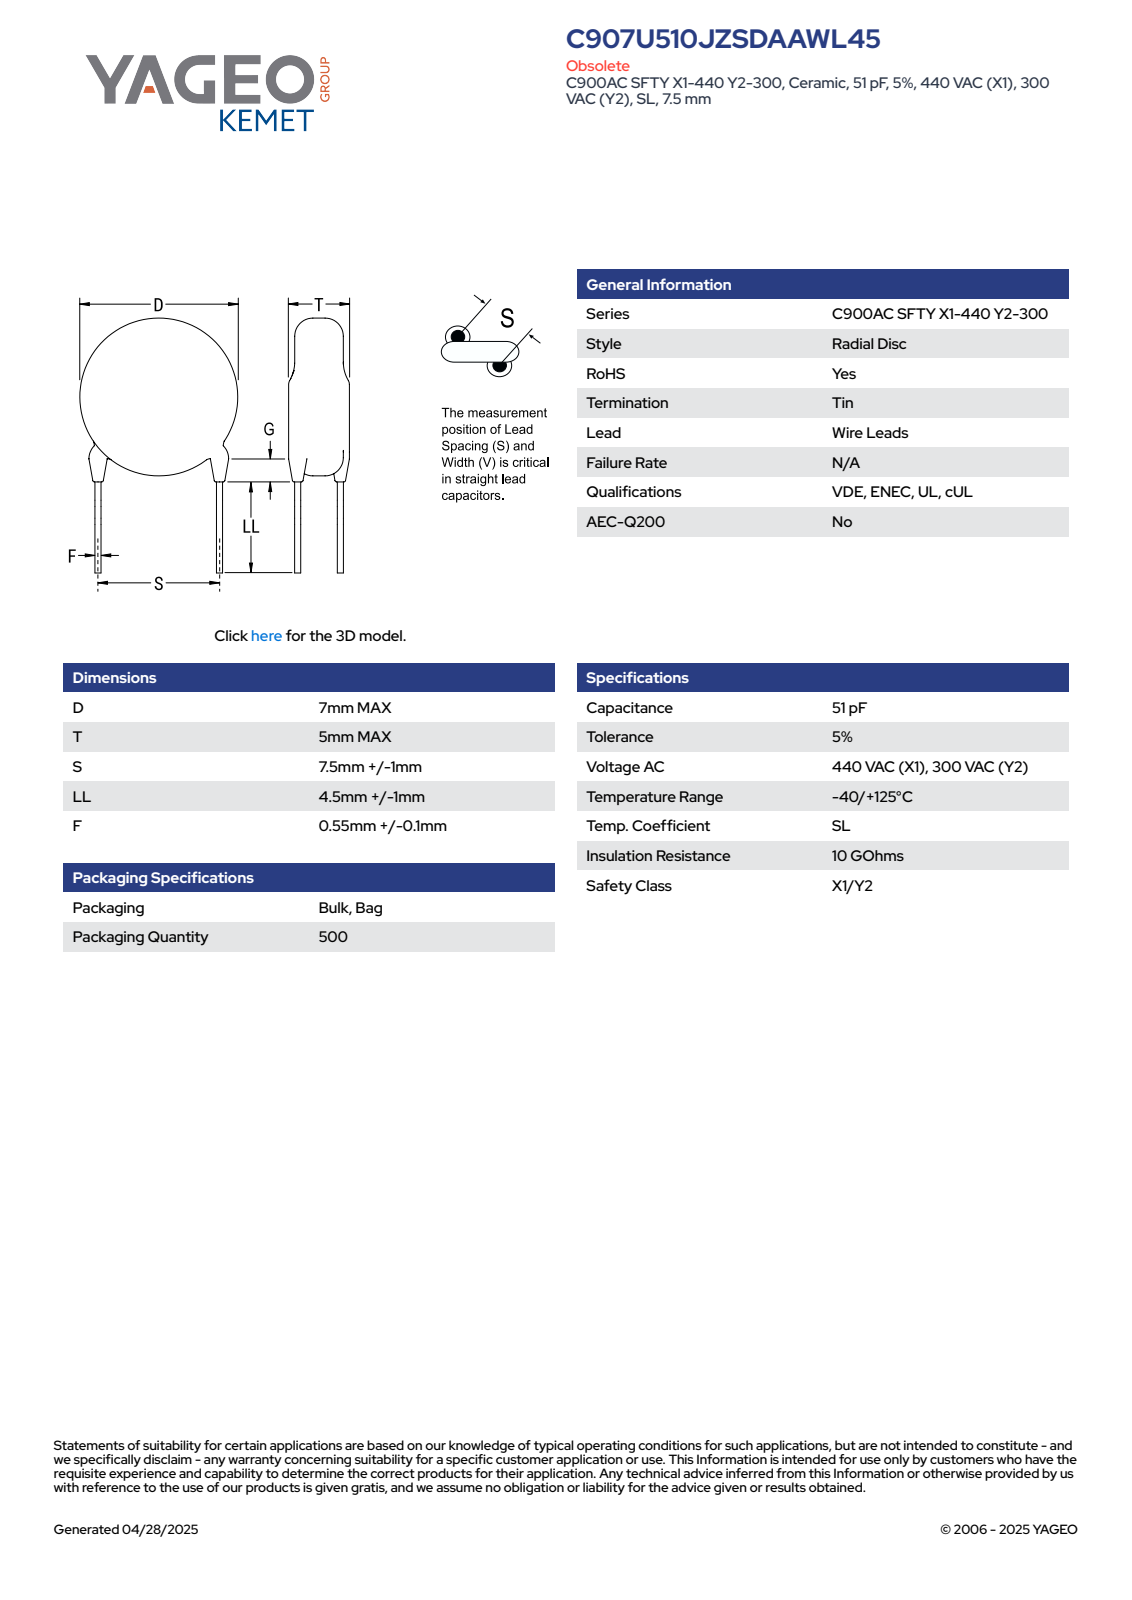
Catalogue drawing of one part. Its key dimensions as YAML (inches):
part_name: "CCD_STC900_D7T5S7.5LL5.5F0.65G3"
step_written_by: "SolidWorks 2014 (AUTOMOTIVE_DESIGN)"
units: inches
bodies: {solids: 4, faces: 83, planar: 61, cylindrical: 6, other: 16}
overall_size: [0.506, 0.304, 0.197]
volume: 0.012
surface_area: 0.315
round_bosses_or_shafts:
  - {diameter: 0.026, count: 2}
  - {diameter: 0.276, count: 1}
face_to_face_distances: [0.197, 0.032, 0.384, 0.352, 0.13, 0.066, 0.139, 0.094, 0.098, 0.052]
